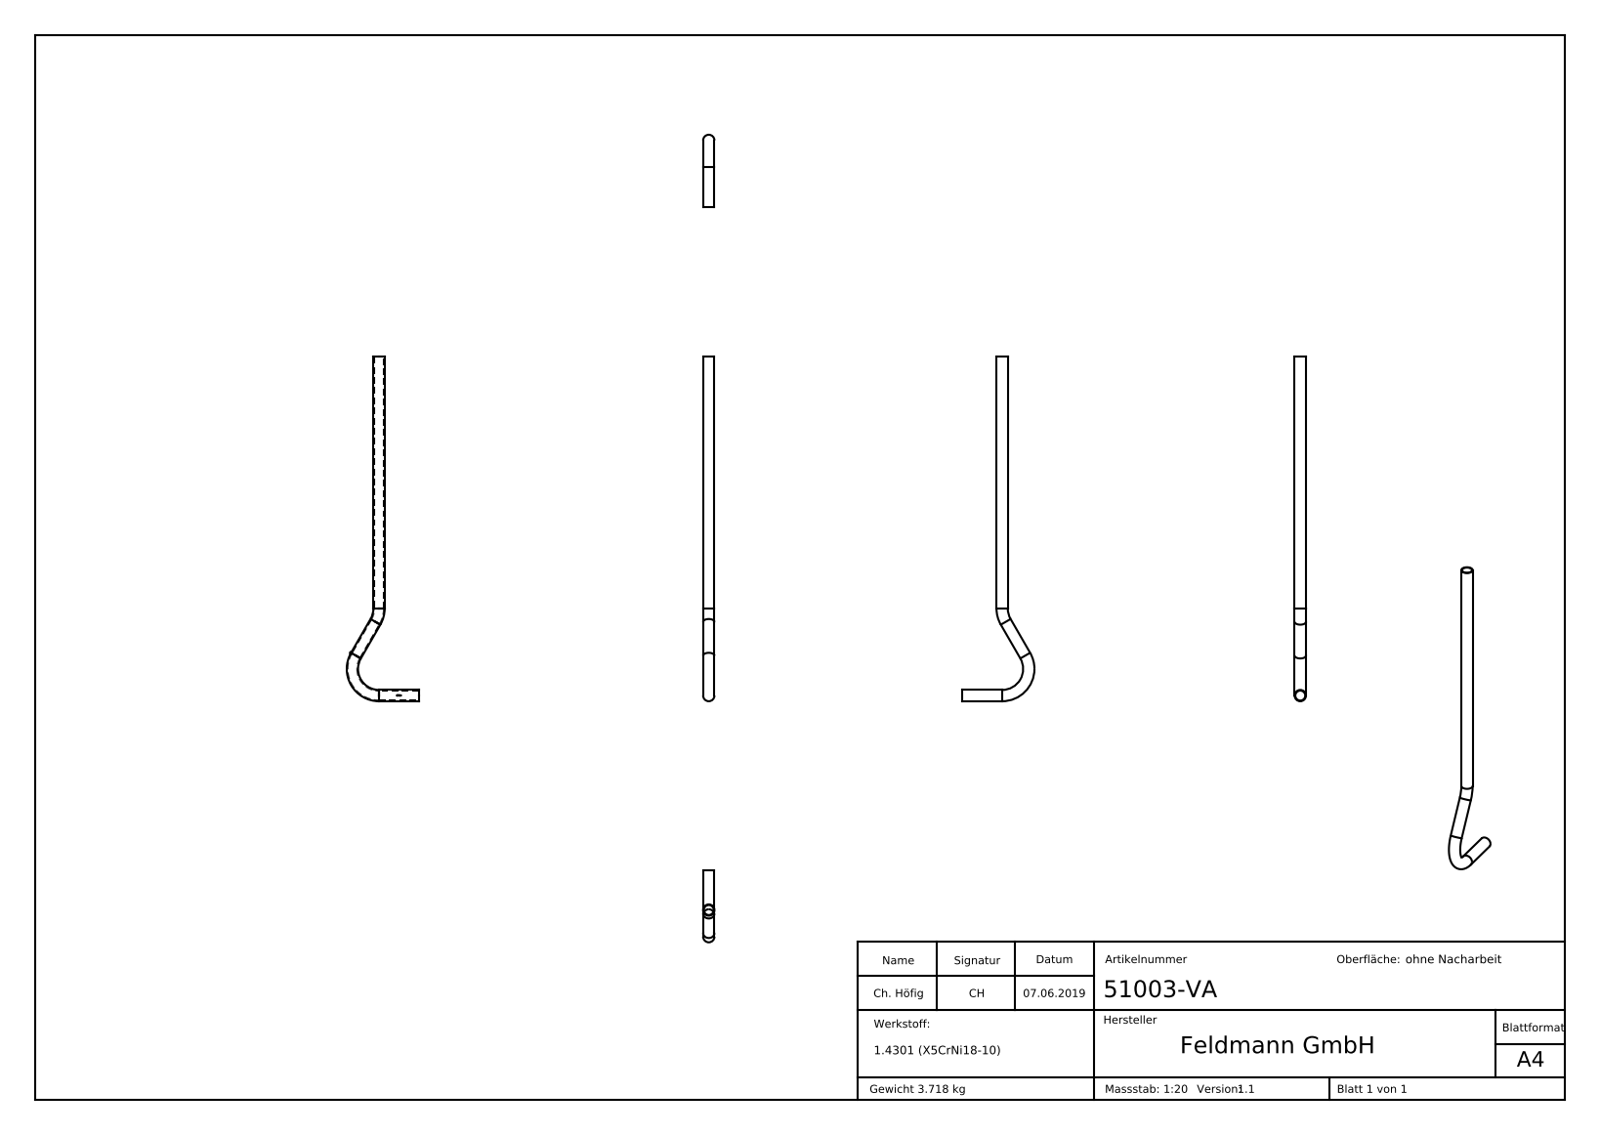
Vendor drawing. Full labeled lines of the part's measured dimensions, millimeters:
Part name (STEP PRODUCT): 51003-VA
STEP written by: SolidWorks 2015 (CONFIG_CONTROL_DESIGN)
Units: millimetres
Bodies: 1 solid, 227 faces (93 planar, 34 cylindrical, 100 other)
Overall size (bounding box): 1292.99 × 270 × 42.4
Volume: 470 688 mm³ · Surface area: 377 187 mm²
Round holes (diameter × count): ⌀37.4 ×3
Round bosses / shafts (diameter × count): ⌀42.4 ×3
Partial cylindrical surfaces — rounded edges, fillets, slot ends (radius × count): R18.8 ×1
Main face-to-face distances: 2.97, 0.39, 5.73, 8.7, 4.09, 1.12, 2.02, 10.72, 1.32, 4.36
